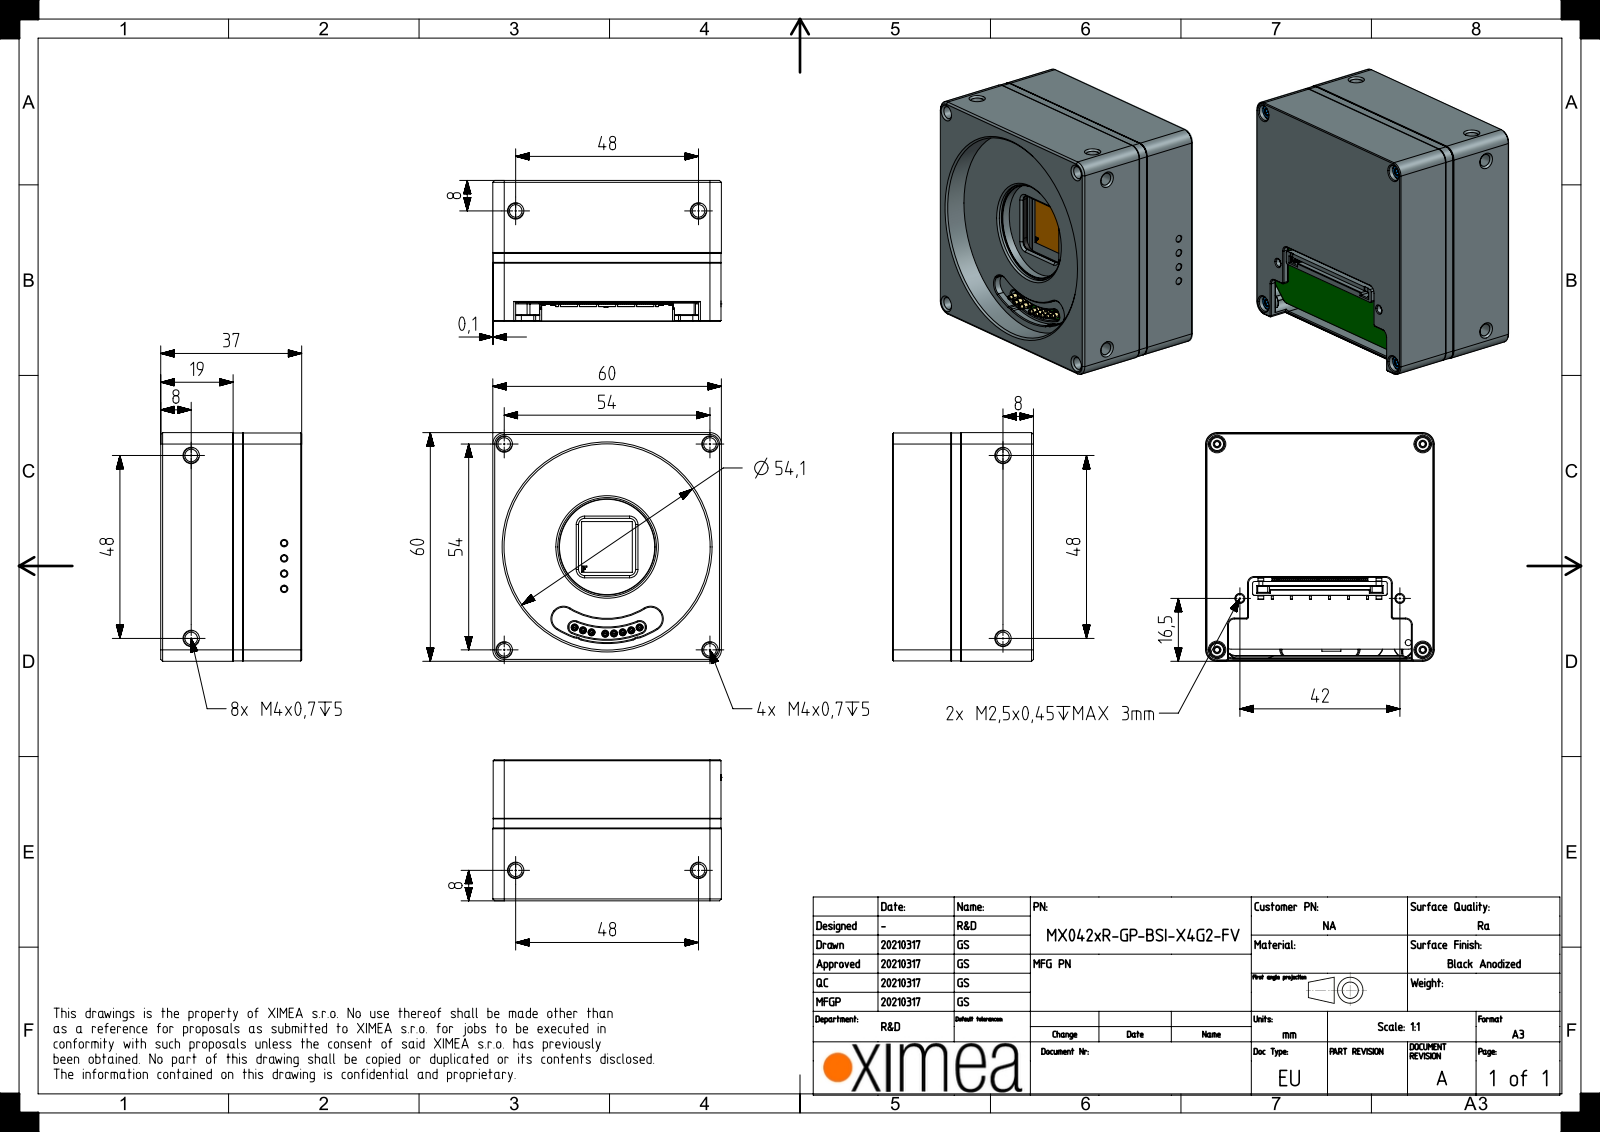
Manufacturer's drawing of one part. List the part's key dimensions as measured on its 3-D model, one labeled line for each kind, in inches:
Part name (STEP PRODUCT): GSENSE2020-GLASS; GSENSE2020-BODY; MX-X4L-MAIN-FV-PCA-LW; MECH-LIGHTPIPE-1.63X4.14 (+8 more)
STEP written by: SIEMENS PLM Software NX 1907 (AUTOMOTIVE_DESIGN)
Units: inches
Bodies: 96 solids, 22968 faces (18052 planar, 3922 cylindrical, 994 other)
Overall size (bounding box): 2.362 × 2.362 × 1.457
Volume: 3.308 in³ · Surface area: 103.8 in²
Round holes (diameter × count): ⌀0.022 ×153, ⌀0.063 ×20, ⌀0.083 ×14, ⌀0.051 ×10, ⌀0.079 ×10, ⌀0.036 ×8, ⌀0.043 ×8, ⌀0.051 ×8, ⌀0.13 ×8, ⌀0.061 ×4, ⌀0.094 ×4, ⌀0.106 ×4
Round bosses / shafts (diameter × count): ⌀0.03 ×153, ⌀0.012 ×153, ⌀0.118 ×9, ⌀0.072 ×8, ⌀0.061 ×8, ⌀0.059 ×8, ⌀0.051 ×8, ⌀0.049 ×8
Partial cylindrical surfaces — rounded edges, fillets, slot ends (radius × count): R0.004 ×134, R0.118 ×67, R0.011 ×60, R0.059 ×56, R0.02 ×47, R0.004 ×30, R0.006 ×30, R0.039 ×21
Main face-to-face distances: 0.035, 2.323, 0.039, 2.358, 0.059, 0.041, 0.417, 0.118, 0.098, 0.394
Hole centre spacings: 0.754, 0.091, 0.896, 0.896, 1.503, 1.631, 1.731, 2.126
